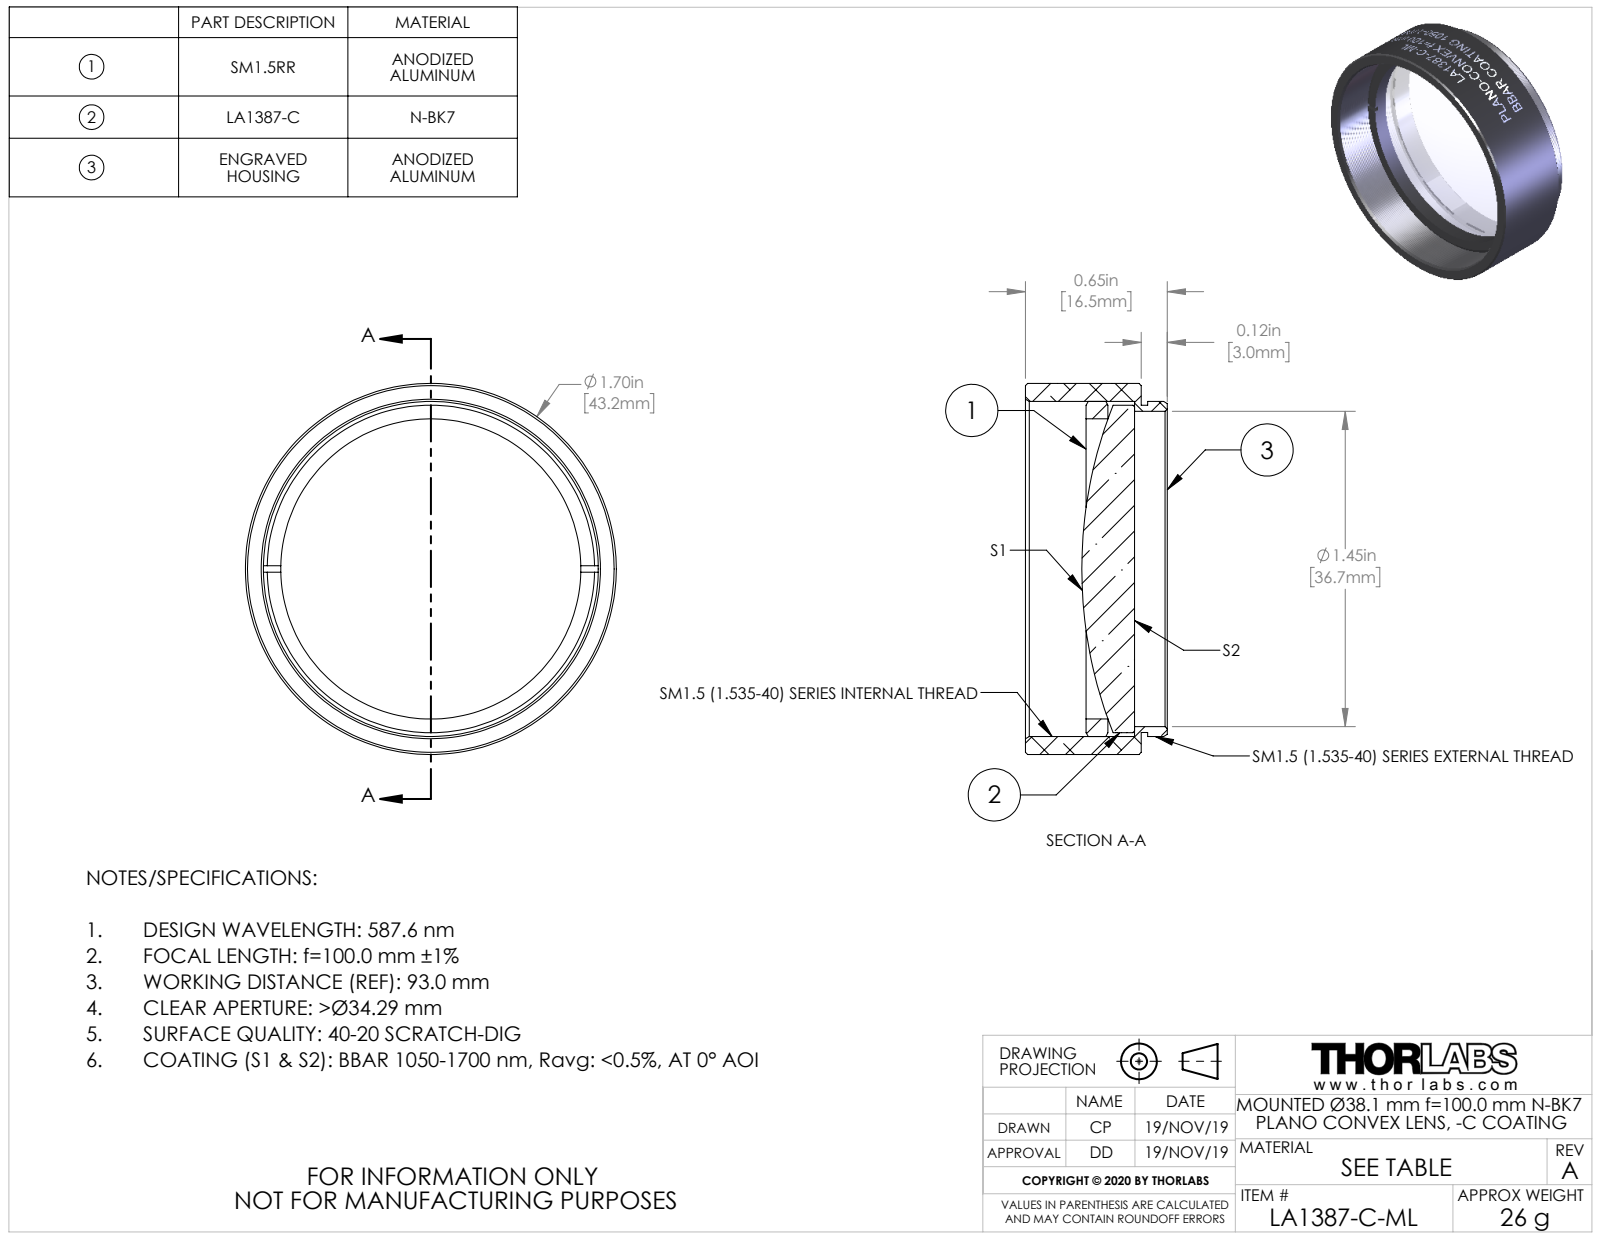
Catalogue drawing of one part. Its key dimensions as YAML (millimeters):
part_name: "TTN200746-E0W"
step_written_by: "SolidWorks 2018 (CONFIG_CONTROL_DESIGN)"
units: millimeters
bodies: {solids: 3, faces: 158, planar: 15, cylindrical: 124, other: 19}
overall_size: [43.18, 43.18, 16.51]
volume: 9623
surface_area: 8639
round_holes:
  - {diameter: 34.92, count: 1}
  - {diameter: 36.7, count: 1}
round_bosses_or_shafts:
  - {diameter: 43.18, count: 1}
  - {diameter: 38.99, count: 1}
  - {diameter: 38.1, count: 1}
  - {diameter: 38.07, count: 1}
face_to_face_distances: [0.76, 13.46, 12.7, 3.86, 3.1, 9.6, 6.4, 5.64, 2.54, 7.06]
